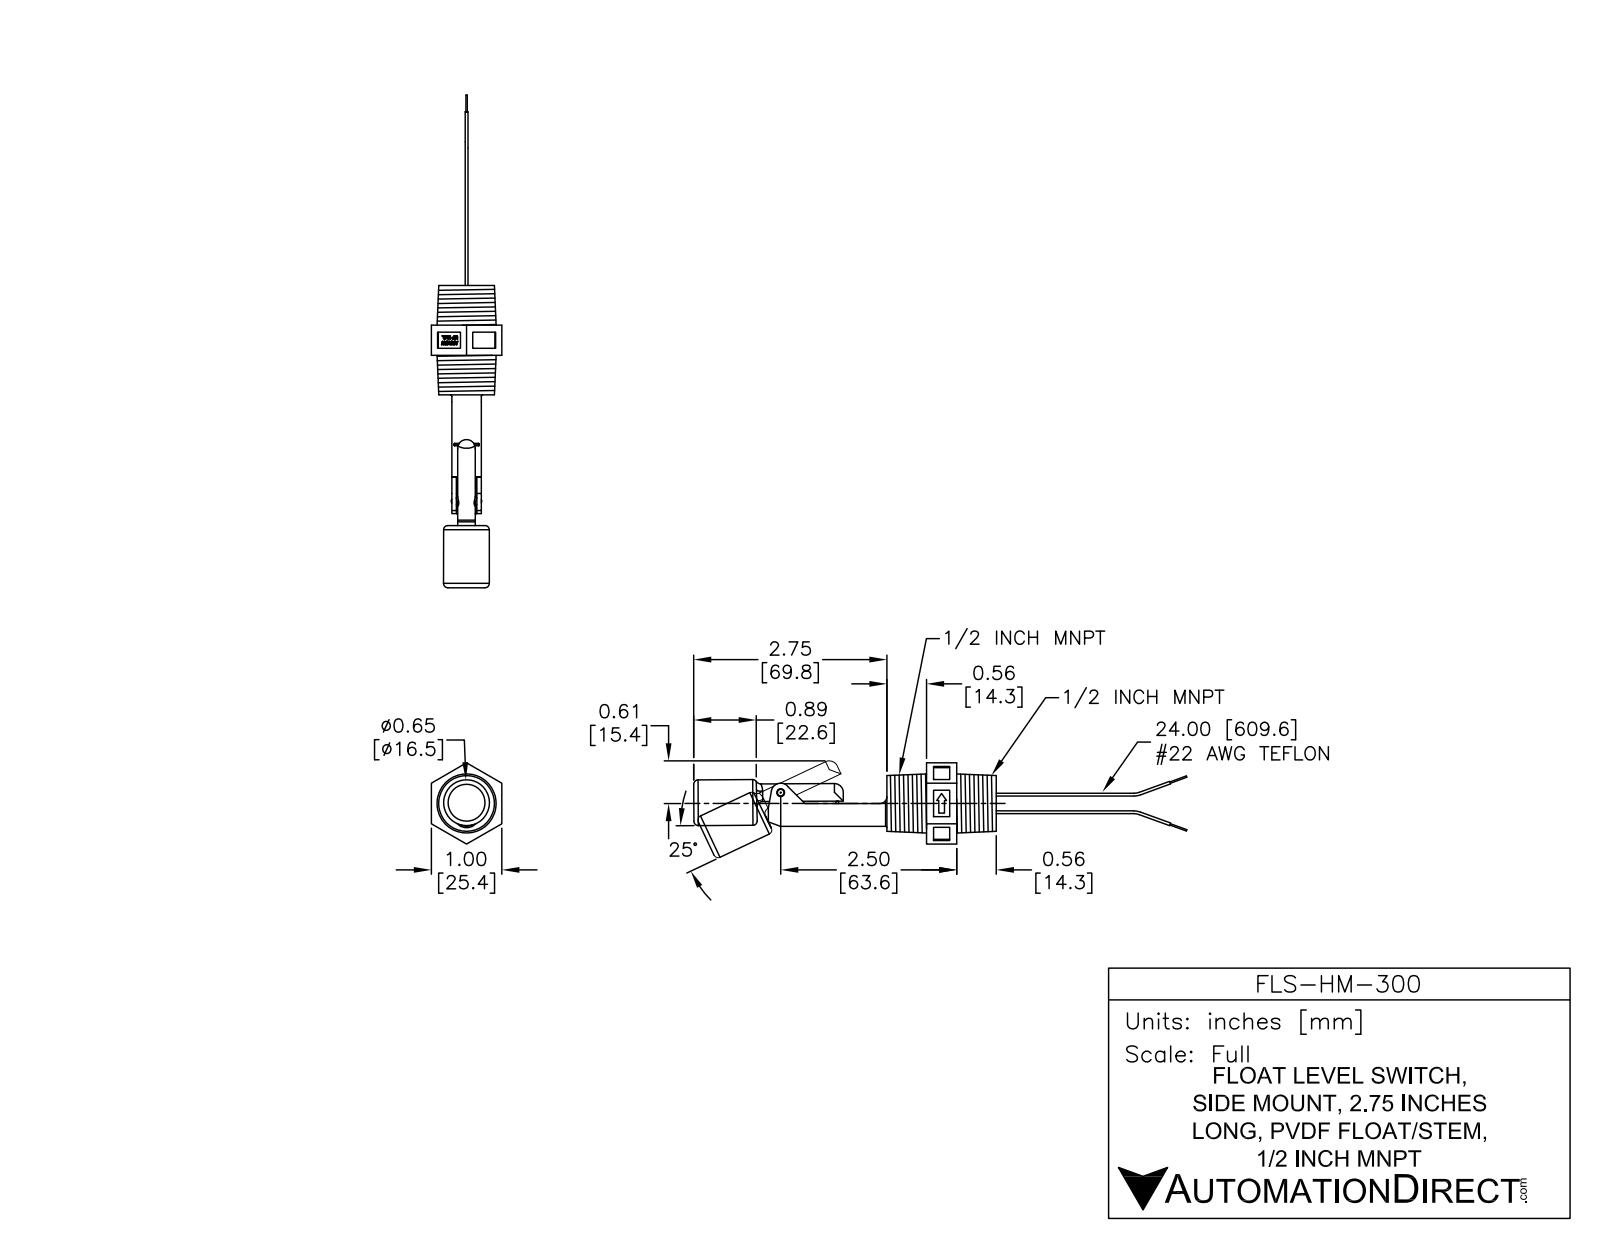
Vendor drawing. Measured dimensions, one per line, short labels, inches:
name: FLS-HM-300
written by: SolidWorks 2013 (AUTOMOTIVE_DESIGN)
unit: in
bodies: 6 solids, 163 faces (88 planar, 41 cylindrical, 34 other)
size: 7.019 × 1.155 × 1
volume: 1.445 in³; area: 14.78 in²
holes: 1× ⌀0.109
bosses: 4× ⌀0.04, 2× ⌀0.02, 1× ⌀0.65, 1× ⌀0.25, 1× ⌀0.1
rounds: 8× R0.01, 2× R0.02, 2× R0.067, 1× R0.1, 1× R0.125, 1× R0.21
face distances: 0.43, 0.02, 0.98, 1, 0.563, 0.993, 1.513, 0.95, 0.52, 0.355
